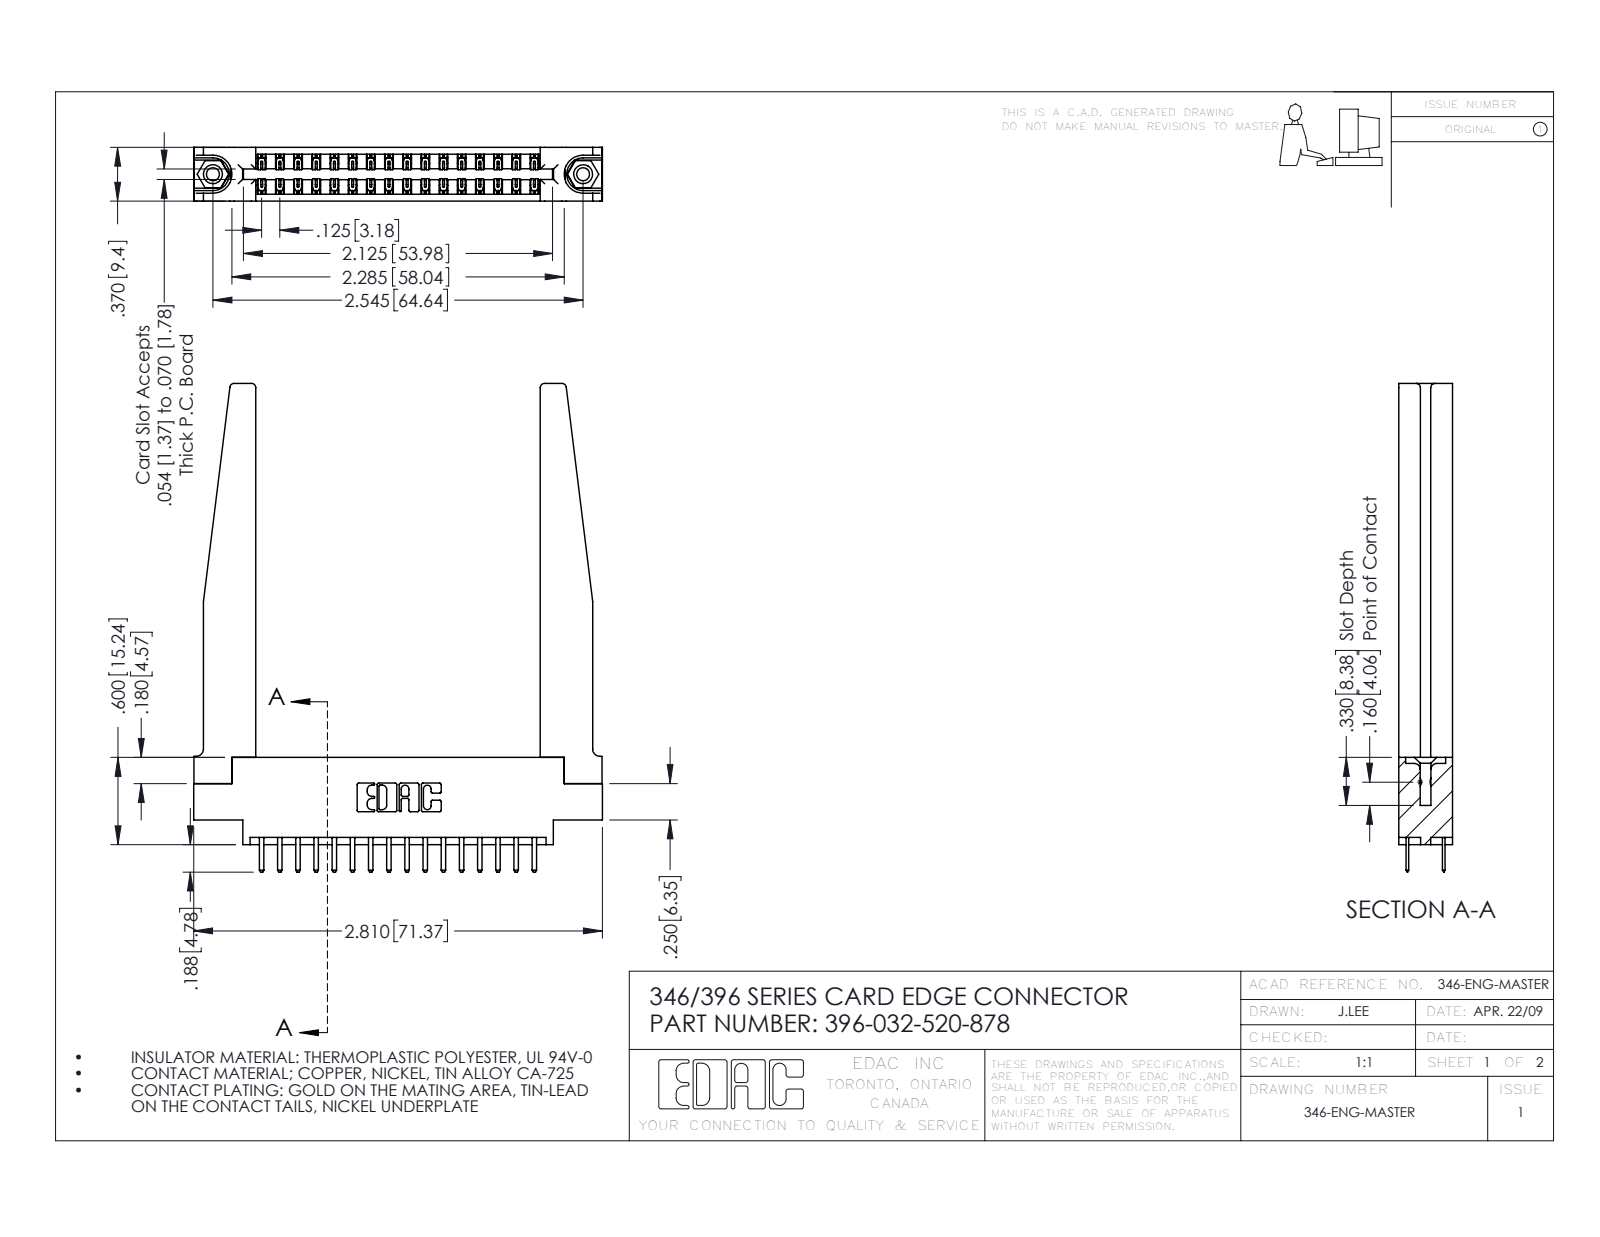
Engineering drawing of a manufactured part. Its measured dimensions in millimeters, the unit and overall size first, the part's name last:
Units: millimetres
Overall size (bounding box): 85.3 × 71.4 × 9.4
Round holes (diameter × count): ⌀2.3 ×2, ⌀3.2 ×2, ⌀4 ×2, ⌀1.6 ×1
Round bosses / shafts (diameter × count): ⌀3.9 ×2
Partial cylindrical surfaces — rounded edges, fillets, slot ends (radius × count): R0.2 ×48, R0.3 ×36, R0.3 ×22, R0.8 ×8, R0.2 ×6, R0.8 ×6, R0.7 ×3, R0.4 ×2
Main face-to-face distances: 9.4, 3.8, 1.8, 3.8, 1.2, 8.2, 6.4, 2.6, 5.6, 4.4
Hole centre spacings: 6.2, 59.4, 64.6
Volume: 13 500 mm³ · Surface area: 15 340 mm²
Bodies: 37 solids, 2152 faces (1406 planar, 694 cylindrical, 52 other)
Part name (STEP PRODUCT): 396-032-520-878; 345-250-001_345-250-001-102; 346-220-078_345-220-078; 346 Part_0.170 Offset - 0.156 Dia-TH (+1 more)
STEP written by: SolidWorks 2016 (CONFIG_CONTROL_DESIGN)
